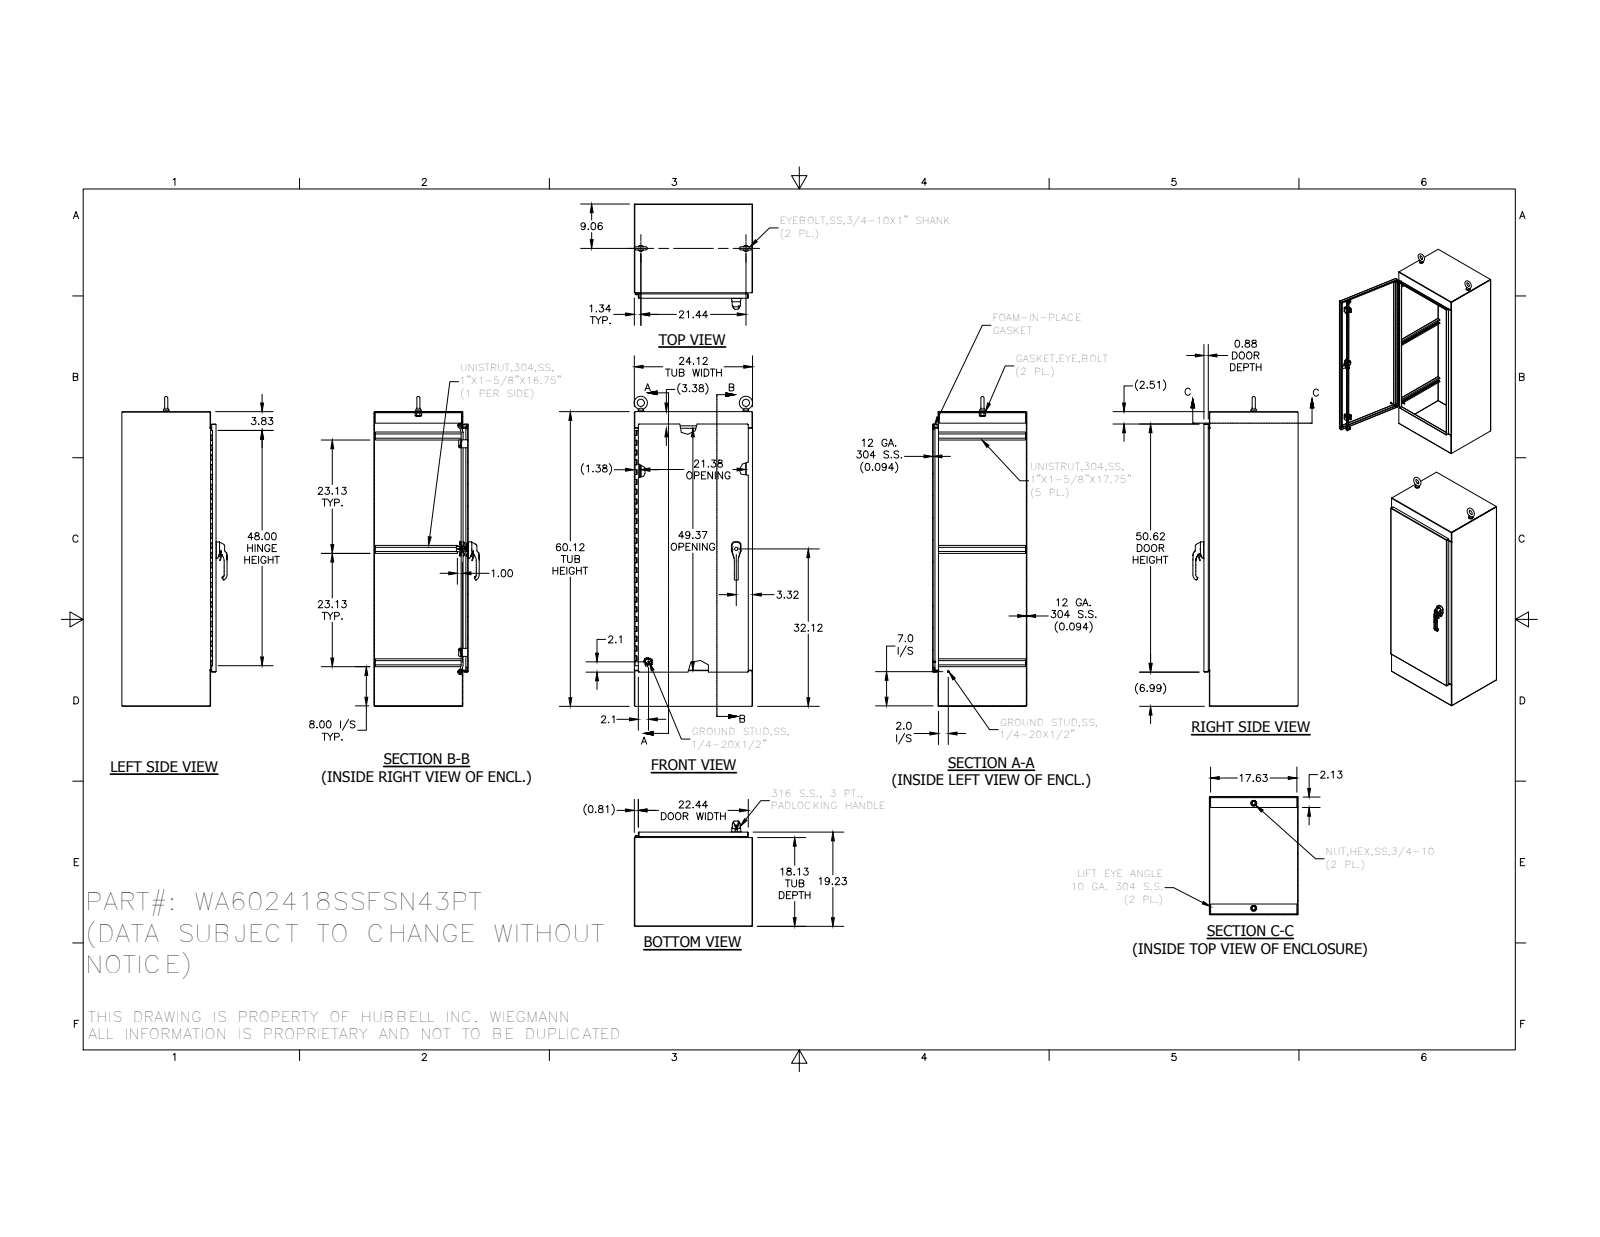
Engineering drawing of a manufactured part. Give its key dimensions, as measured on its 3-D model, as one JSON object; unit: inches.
{"part_name": "WA602418SSFSN43PT; HFW31235; WA6024SSFSN43PT-DR; 37028 (+8 more)", "step_written_by": "SolidWorks 2014 (AUTOMOTIVE_DESIGN)", "units": "inches", "bodies": {"solids": 64, "faces": 3387, "planar": 1166, "cylindrical": 1281, "other": 940}, "overall_size": [63.248, 24.125, 21.476], "volume_in3": 713.2, "surface_area_in2": 14648, "round_holes": [[0.262, 8], [0.375, 8], [0.187, 4], [0.213, 3], [0.25, 3], [0.28, 3], [0.241, 2], [0.252, 2], [0.315, 2], [0.4, 2], [0.402, 2], [0.413, 2]], "round_bosses_or_shafts": [[1, 3], [0.236, 3], [1.25, 2], [1.12, 2], [0.75, 2], [0.563, 2], [0.533, 2], [0.531, 2]], "partial_cylinders_radius": [[0.02, 172], [0.012, 107], [0.125, 26], [0.019, 21], [0.031, 19], [0.05, 19], [0.125, 15], [0.079, 14]], "face_to_face_distances": [0.094, 19.133, 24.031, 19.039, 23.937, 19.227, 24.125, 60.031, 18.031, 1.102], "hole_center_spacings": [5.333, 16, 0.38, 0.76, 10.667, 21.333, 0.38, 0.492]}
